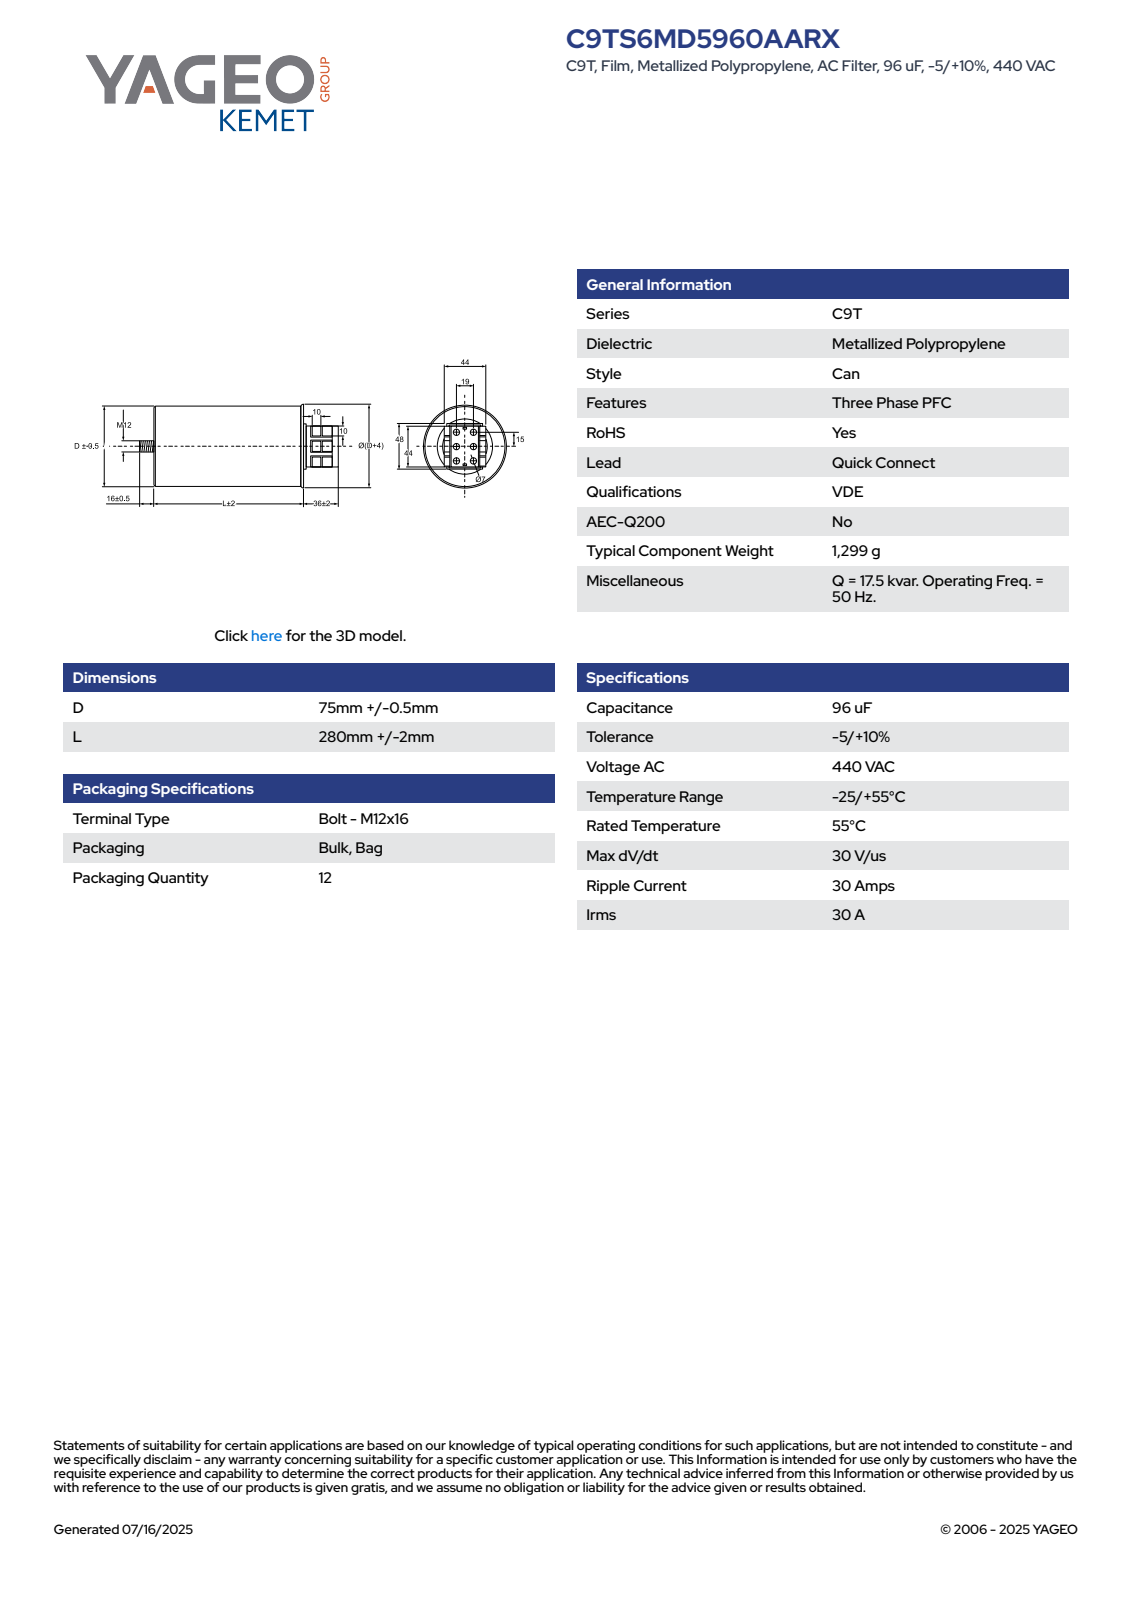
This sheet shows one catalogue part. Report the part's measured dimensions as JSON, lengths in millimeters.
{"part_name": "CFP_C9T_75X280_D75.5L282", "step_written_by": "SolidWorks 2014 (AUTOMOTIVE_DESIGN)", "units": "millimeters", "bodies": {"solids": 1, "faces": 132, "planar": 78, "cylindrical": 19, "other": 35}, "overall_size": [336.5, 79.5, 79.5], "volume_mm3": 1300000, "surface_area_mm2": 98089, "round_holes": [[7, 6]], "round_bosses_or_shafts": [[75.5, 1], [12, 1]], "partial_cylinders_radius": [[37.76, 1]], "face_to_face_distances": [10, 11.15, 282, 15.85, 1.15, 4, 44, 286, 38, 32.85], "hole_center_spacings": [15, 24.21, 19, 30, 35.51]}
